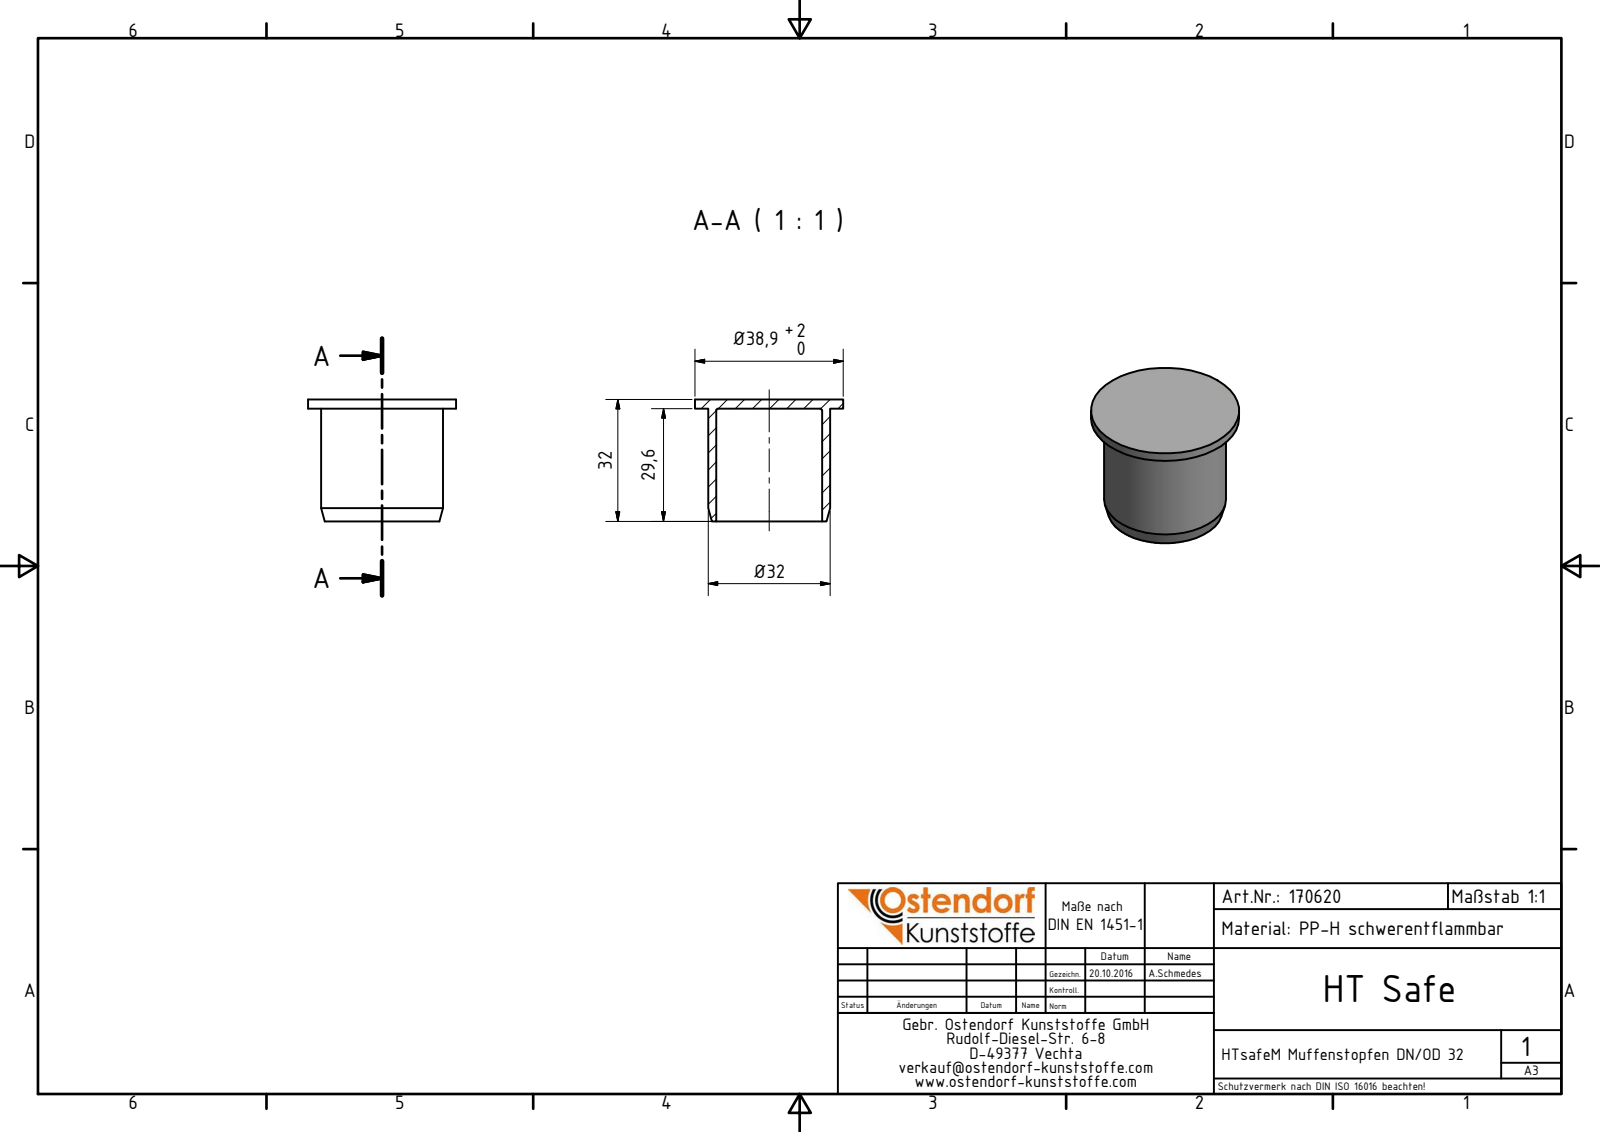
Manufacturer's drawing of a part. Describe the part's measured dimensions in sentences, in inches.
The part is named "170620 HTsafeM DN_OD 32". Its 3-D file was written by "Autodesk Inventor 2016 (AUTOMOTIVE_DESIGN)". It is 1 solid with 9 faces: 4 planar, 3 cylindrical and 2 other. Overall it measures 1.531 by 1.531 by 1.26 inches. Its volume is 0.521 cubic inches and its surface area 12.59 square inches. Round holes: 1 of diameter 1.094. Round bosses or shafts: 1 of diameter 1.531, 1 of diameter 1.26. The main face-to-face distances are 0.094, 1.165, 1.26.
